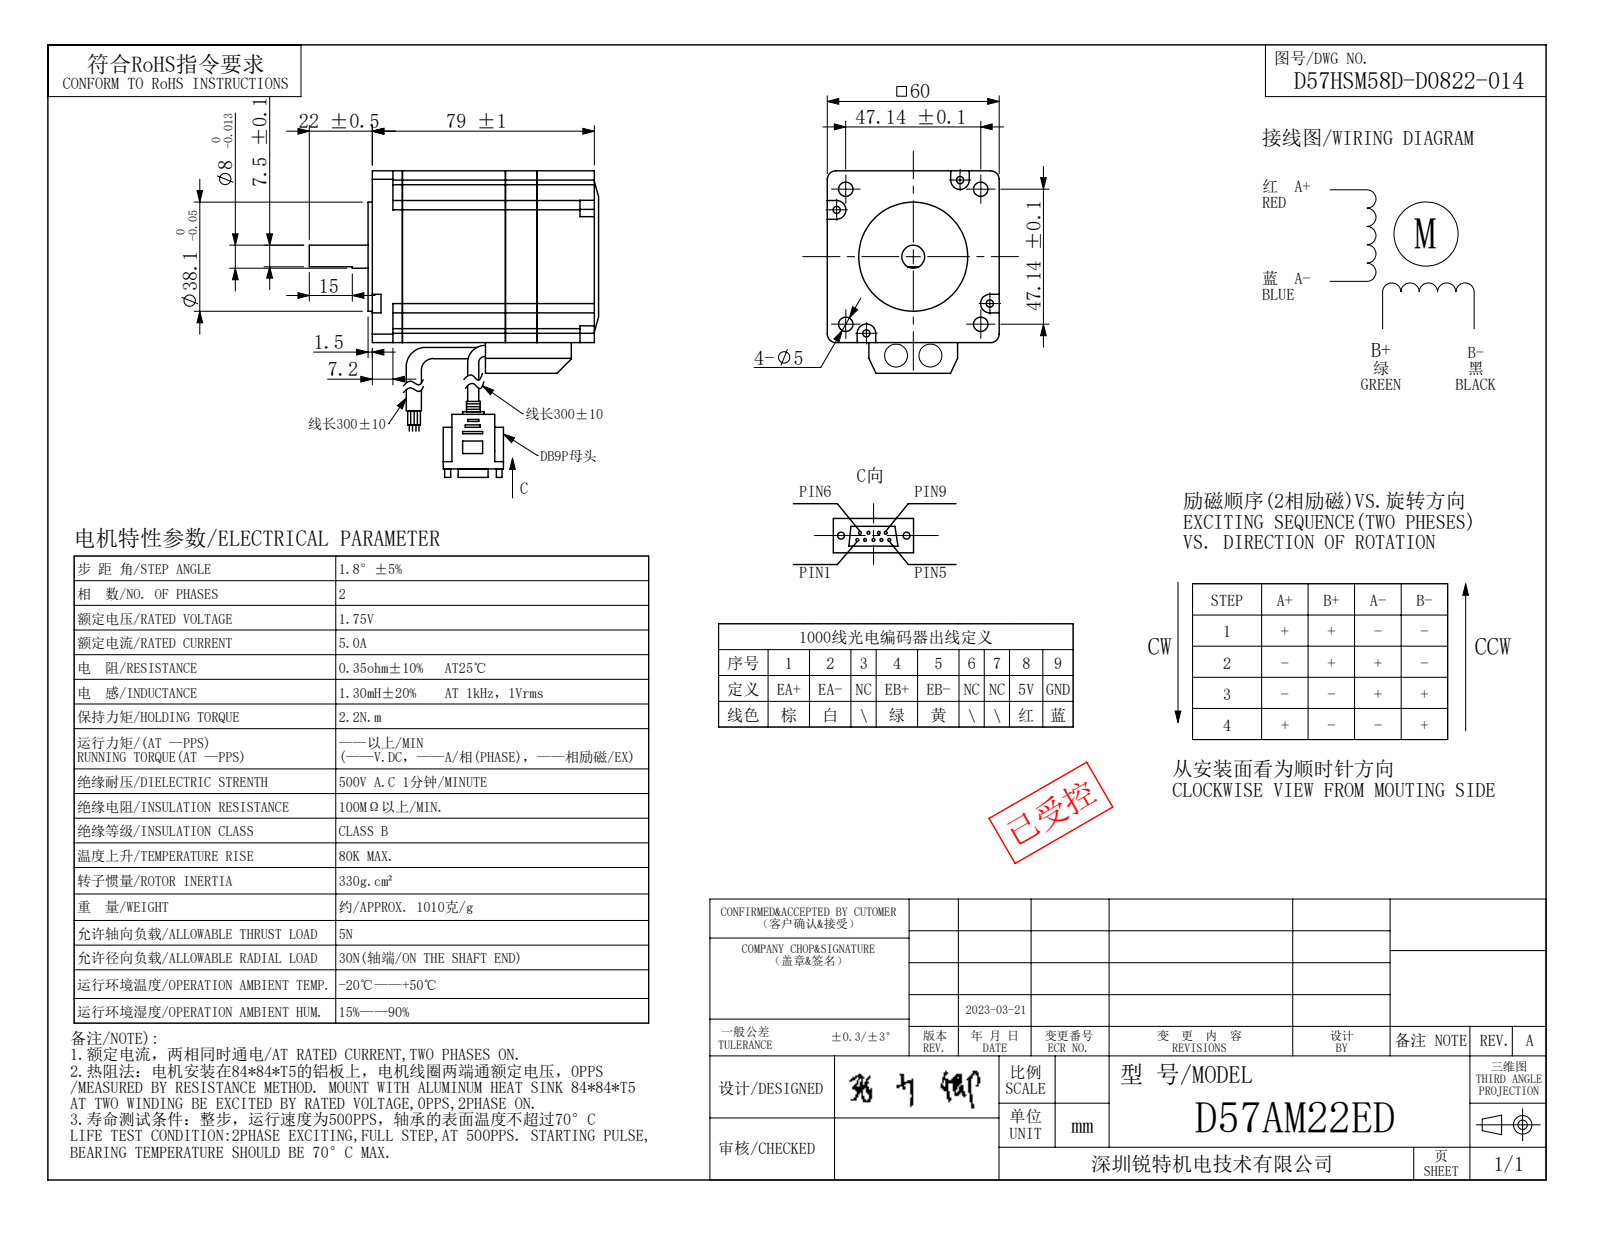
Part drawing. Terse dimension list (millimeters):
written by: SolidWorks 2014 (AUTOMOTIVE_DESIGN)
unit: mm
bodies: 5 solids, 322 faces (165 planar, 153 cylindrical, 4 other)
size: 101 × 70.7 × 60
volume: 113 323 mm³; area: 60 732 mm²
holes: 4× ⌀2.5, 4× ⌀3.5, 4× ⌀3.8, 4× ⌀5, 1× ⌀13, 1× ⌀15.4, 1× ⌀17.8, 1× ⌀18, 1× ⌀22, 1× ⌀50, 1× ⌀50.3, 1× ⌀56
bosses: 1× ⌀52, 1× ⌀40, 1× ⌀39, 1× ⌀38.1, 1× ⌀8
rounds: 8× R3.25, 4× R2.6, 4× R3, 4× R3.3, 4× R5.5
face distances: 60, 79, 57.5, 2.6, 8.4, 74.5, 44.4, 1.5, 17, 2
hole spacings: 7.89, 31.35, 40.05, 50.84, 64.23, 44.34, 33.33, 47.14
